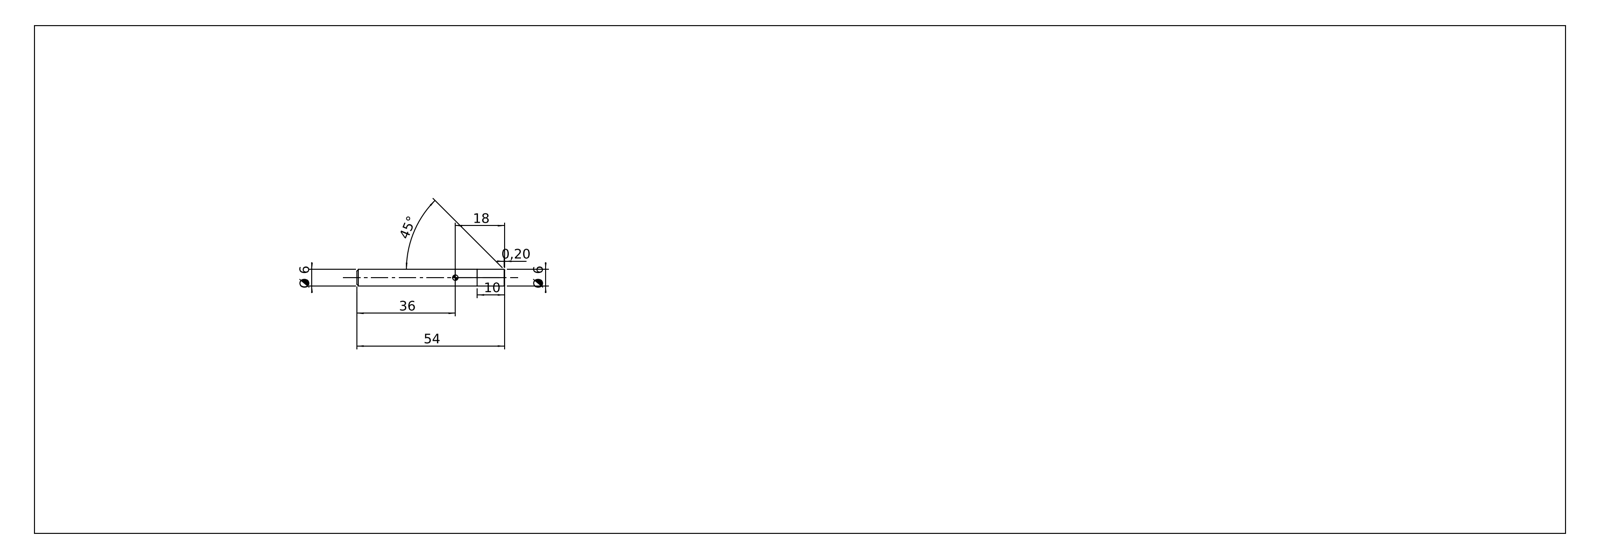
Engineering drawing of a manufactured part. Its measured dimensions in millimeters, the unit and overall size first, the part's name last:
Units: millimetres
Overall size (bounding box): 54 × 6 × 6
Round bosses / shafts (diameter × count): ⌀6 ×1
Main face-to-face distances: 10, 54, 44
Volume: 1 523 mm³ · Surface area: 1 122 mm²
Bodies: 2 solids, 8 faces (4 planar, 2 cylindrical, 2 other)
Part name (STEP PRODUCT): 731.060.00
STEP written by: SolidWorks 2019 (CONFIG_CONTROL_DESIGN)
